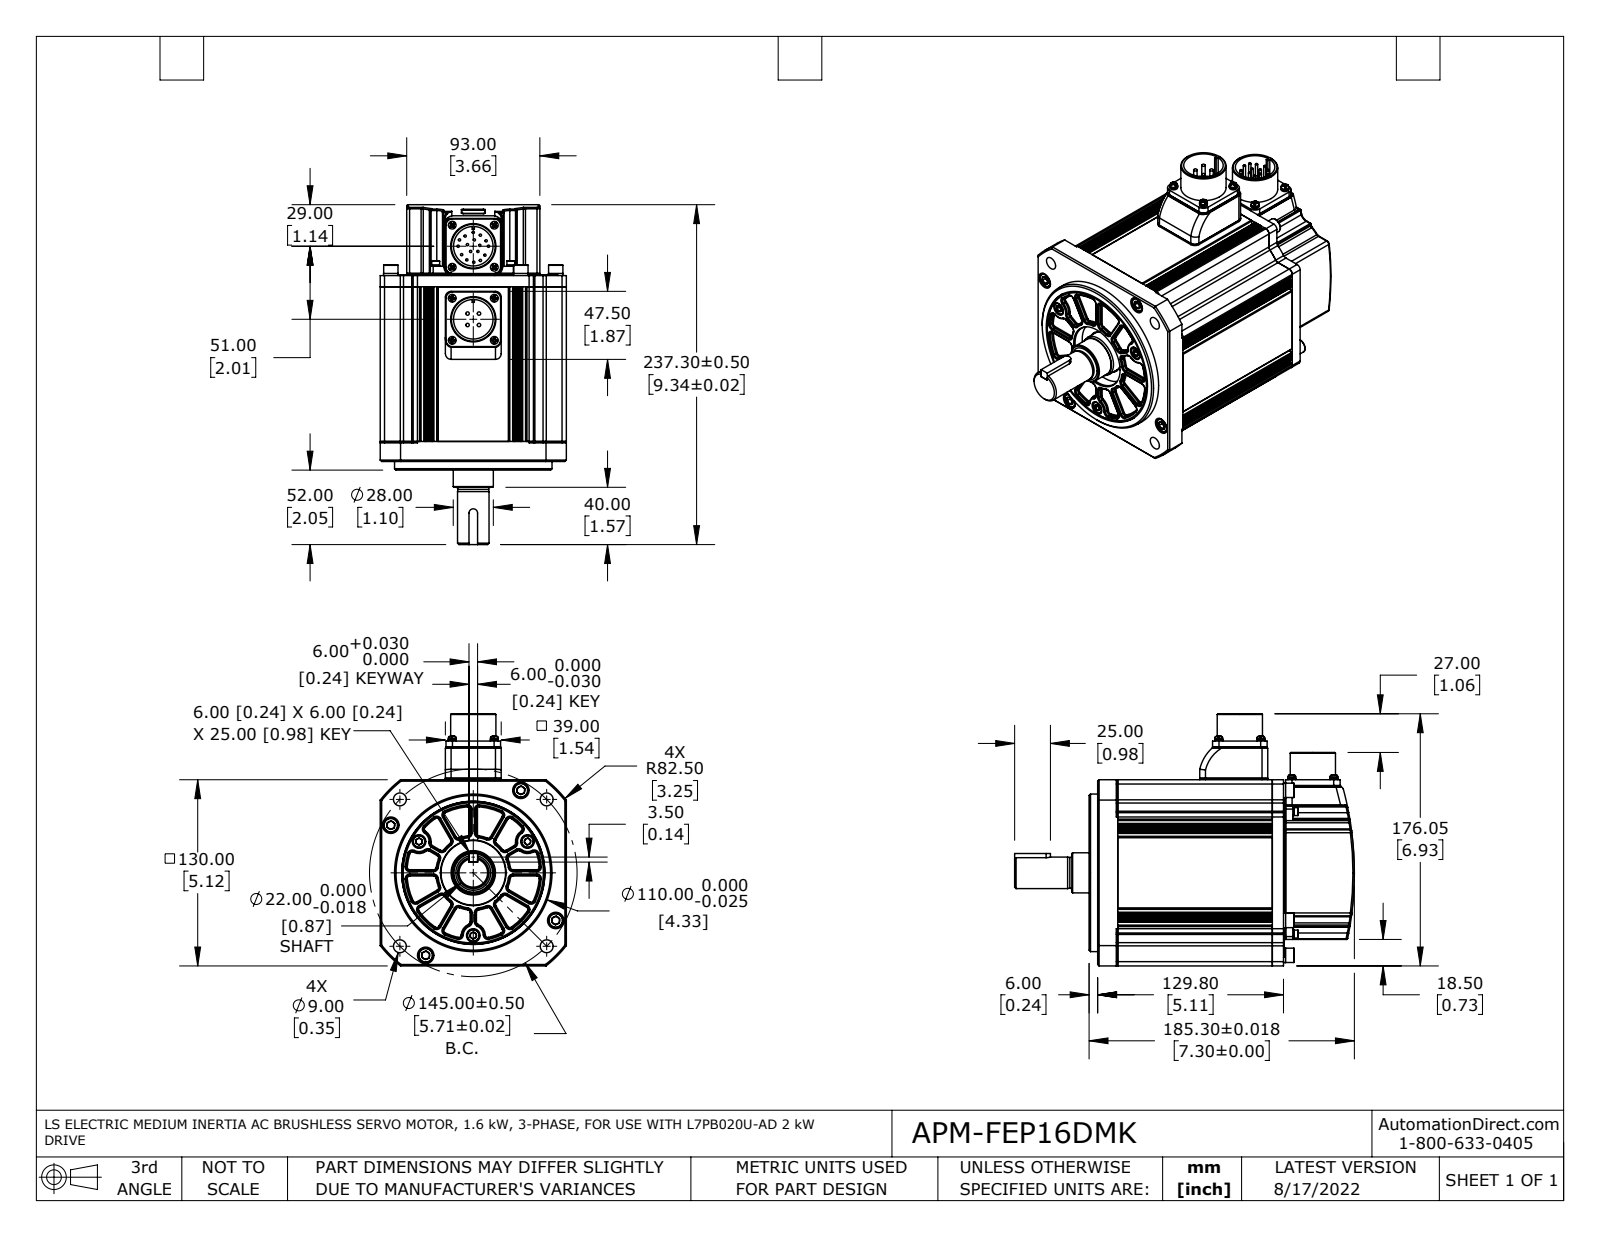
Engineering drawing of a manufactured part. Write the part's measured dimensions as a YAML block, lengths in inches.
part_name: "FMP13GA001G03_Out Line(APM-FEP16D_K) r1 nc fxt"
step_written_by: "SolidWorks 2017 (AUTOMOTIVE_DESIGN)"
units: inches
bodies: {solids: 56, faces: 2131, planar: 706, cylindrical: 801, other: 624}
overall_size: [9.343, 6.931, 5.118]
volume: 148.4
surface_area: 468.4
round_holes:
  - {diameter: 0.098, count: 12}
  - {diameter: 0.118, count: 8}
  - {diameter: 0.12, count: 8}
  - {diameter: 0.138, count: 8}
  - {diameter: 0.197, count: 7}
  - {diameter: 0.142, count: 4}
  - {diameter: 0.146, count: 4}
  - {diameter: 0.268, count: 4}
  - {diameter: 0.276, count: 4}
  - {diameter: 0.354, count: 4}
  - {diameter: 0.453, count: 4}
  - {diameter: 0.22, count: 3}
round_bosses_or_shafts:
  - {diameter: 0.063, count: 17}
  - {diameter: 0.213, count: 8}
  - {diameter: 0.402, count: 4}
  - {diameter: 0.394, count: 4}
  - {diameter: 0.236, count: 4}
  - {diameter: 0.217, count: 4}
  - {diameter: 0.118, count: 4}
  - {diameter: 0.094, count: 4}
partial_cylinders:
  - {radius: 0.02, count: 72}
  - {radius: 0.098, count: 54}
  - {radius: 0.028, count: 24}
  - {radius: 0.079, count: 17}
  - {radius: 0.118, count: 17}
  - {radius: 0.039, count: 14}
  - {radius: 0.177, count: 12}
  - {radius: 0.157, count: 8}
face_to_face_distances: [4.252, 0.039, 5.118, 4.618, 0.327, 4.579, 0.366, 5.031, 4.992, 4.665]
hole_center_spacings: [0.819, 1.157, 2.008, 0.752, 1.041, 1.542, 1.637, 1.975]
